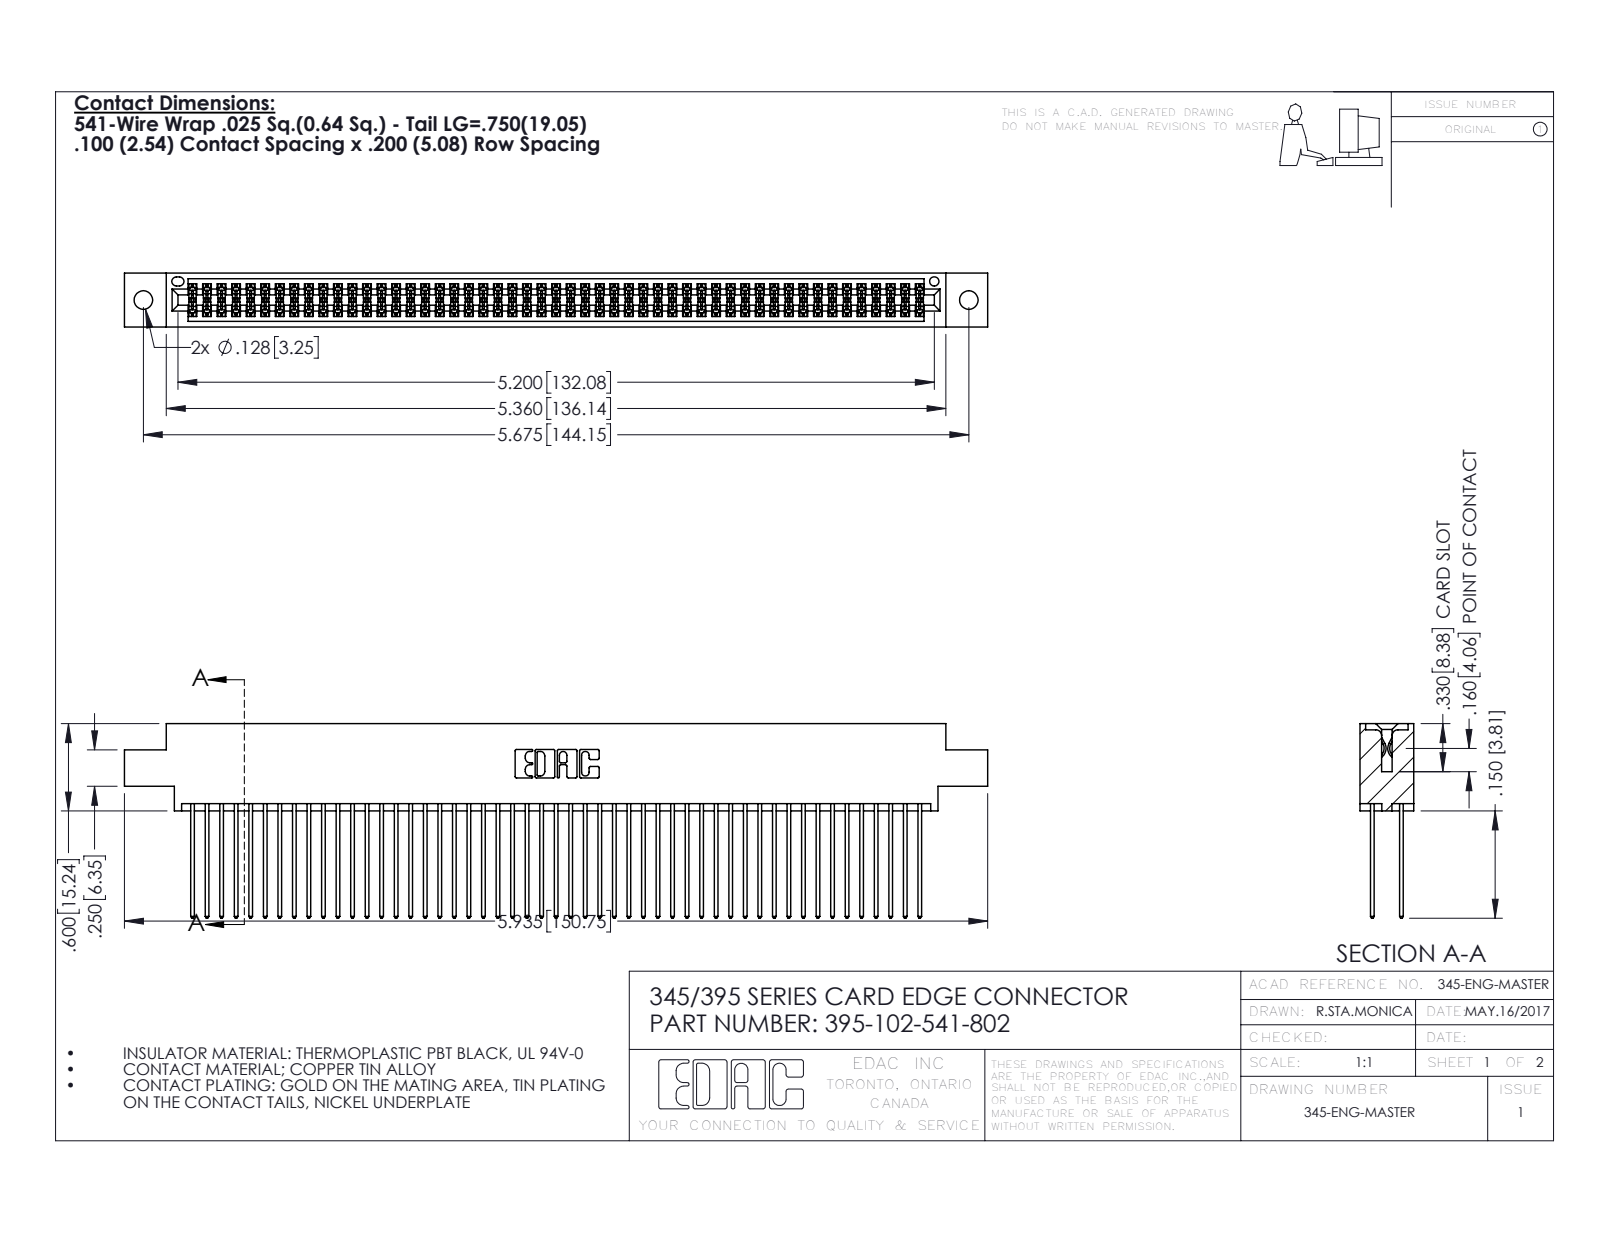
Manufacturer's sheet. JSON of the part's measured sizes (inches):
{"part_name": "345-292-001_345-293-141; 345 Part_0.170 Offset - 0.128 Dia; 395-102-541-802", "step_written_by": "SolidWorks 2016 (CONFIG_CONTROL_DESIGN)", "units": "inches", "bodies": {"solids": 103, "faces": 5230, "planar": 3450, "cylindrical": 1780, "other": 0}, "overall_size": [5.935, 1.337, 0.37], "volume_in3": 0.925, "surface_area_in2": 39.07, "round_holes": [[0.128, 2], [0.064, 1]], "partial_cylinders_radius": [[0.006, 153], [0.01, 102], [0.01, 22], [0.007, 6], [0.031, 6], [0.026, 3], [0.014, 2], [0.019, 2]], "face_to_face_distances": [0.298, 0.072, 0.2, 0.098, 0.272, 0.025, 0.225, 0.37, 0.175, 0.149], "hole_center_spacings": [0.27, 5.439, 5.675]}
